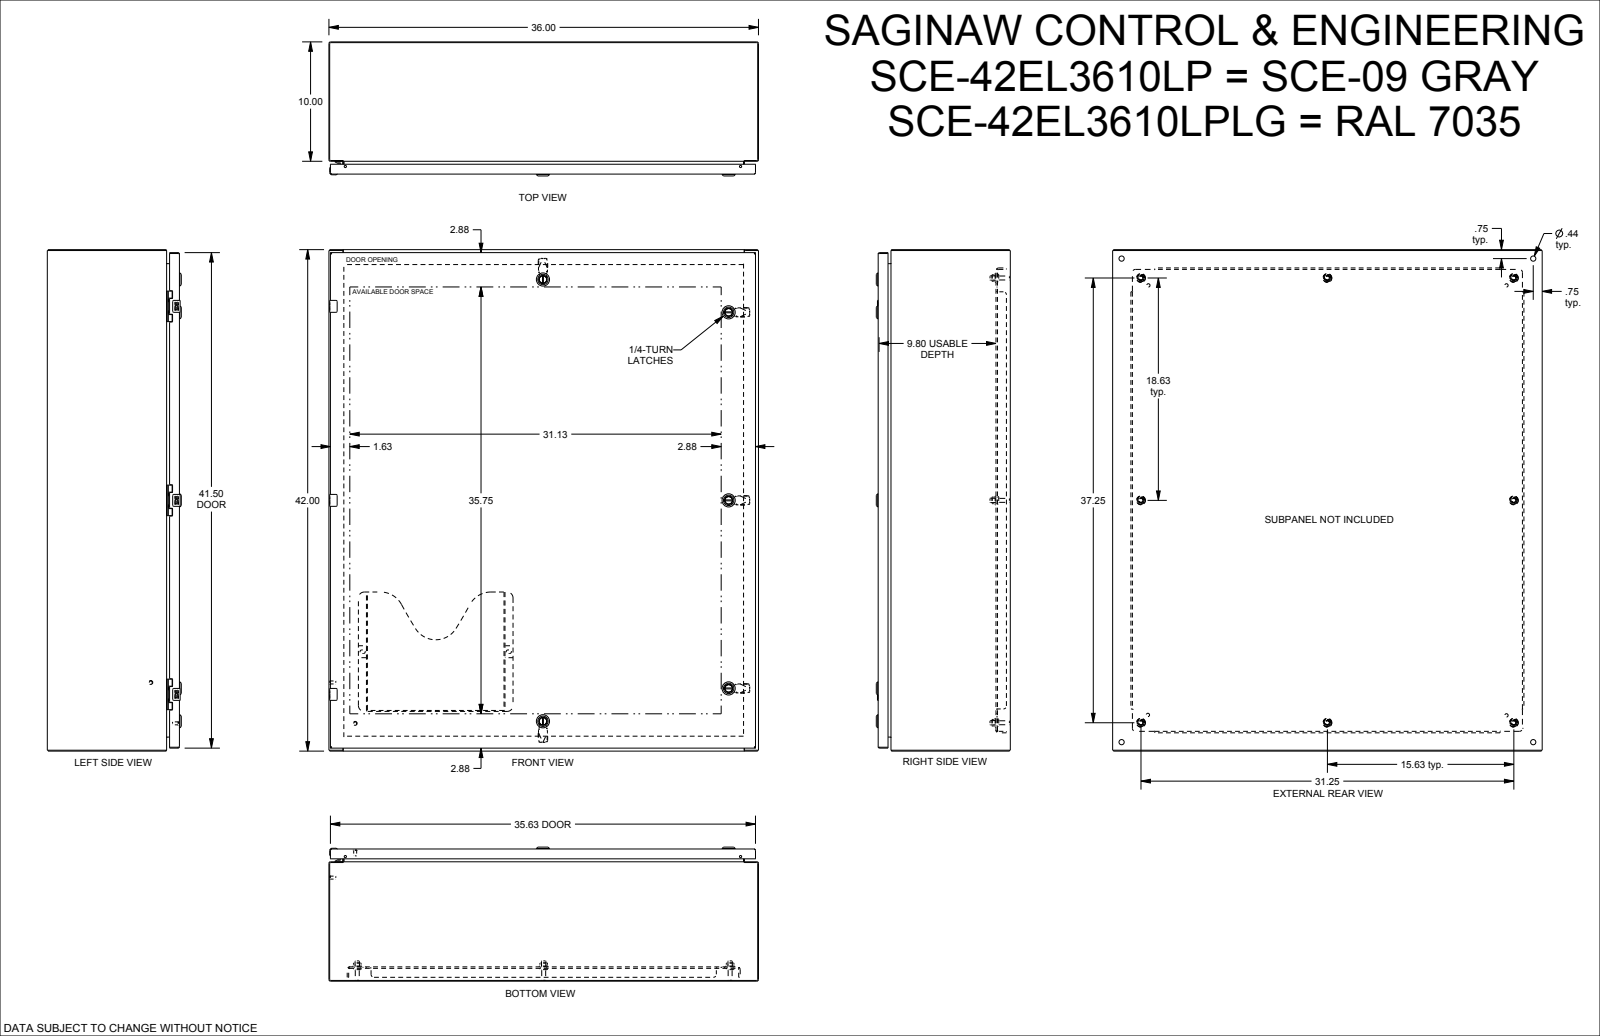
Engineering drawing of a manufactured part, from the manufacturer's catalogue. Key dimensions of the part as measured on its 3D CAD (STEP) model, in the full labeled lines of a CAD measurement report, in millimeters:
Part name (STEP PRODUCT): SCE-42EL3610LPLG
STEP written by: SolidWorks 2019 (CONFIG_CONTROL_DESIGN)
Units: millimetres
Bodies: 0 solids, 4774 faces (2327 planar, 1328 cylindrical, 1119 other)
Overall size (bounding box): 1066.8 × 914.4 × 285.2
Round holes (diameter × count): ⌀9.3 ×8, ⌀12.7 ×8, ⌀4.4 ×6, ⌀5.2 ×6, ⌀6.2 ×6, ⌀6.8 ×6, ⌀9.5 ×6, ⌀5 ×5, ⌀8 ×5, ⌀10 ×5, ⌀16.1 ×5, ⌀7.1 ×4
Round bosses / shafts (diameter × count): ⌀4.3 ×9, ⌀9.3 ×8, ⌀8.4 ×8, ⌀6.4 ×6, ⌀6.1 ×6, ⌀28 ×5, ⌀22 ×5, ⌀20.4 ×5
Partial cylindrical surfaces — rounded edges, fillets, slot ends (radius × count): R0.3 ×136, R0.3 ×52, R0.5 ×52, R0.4 ×32, R4 ×20, R1 ×17, R0.6 ×16, R2.5 ×16
Main face-to-face distances: 1.9, 1.9, 277.4, 279.3, 281.3, 279.3, 30.5, 250.8, 25.4, 28.6
Hole centre spacings: 412.8, 25, 825.5, 0.5, 12.5, 12.5, 114.1, 387.7
